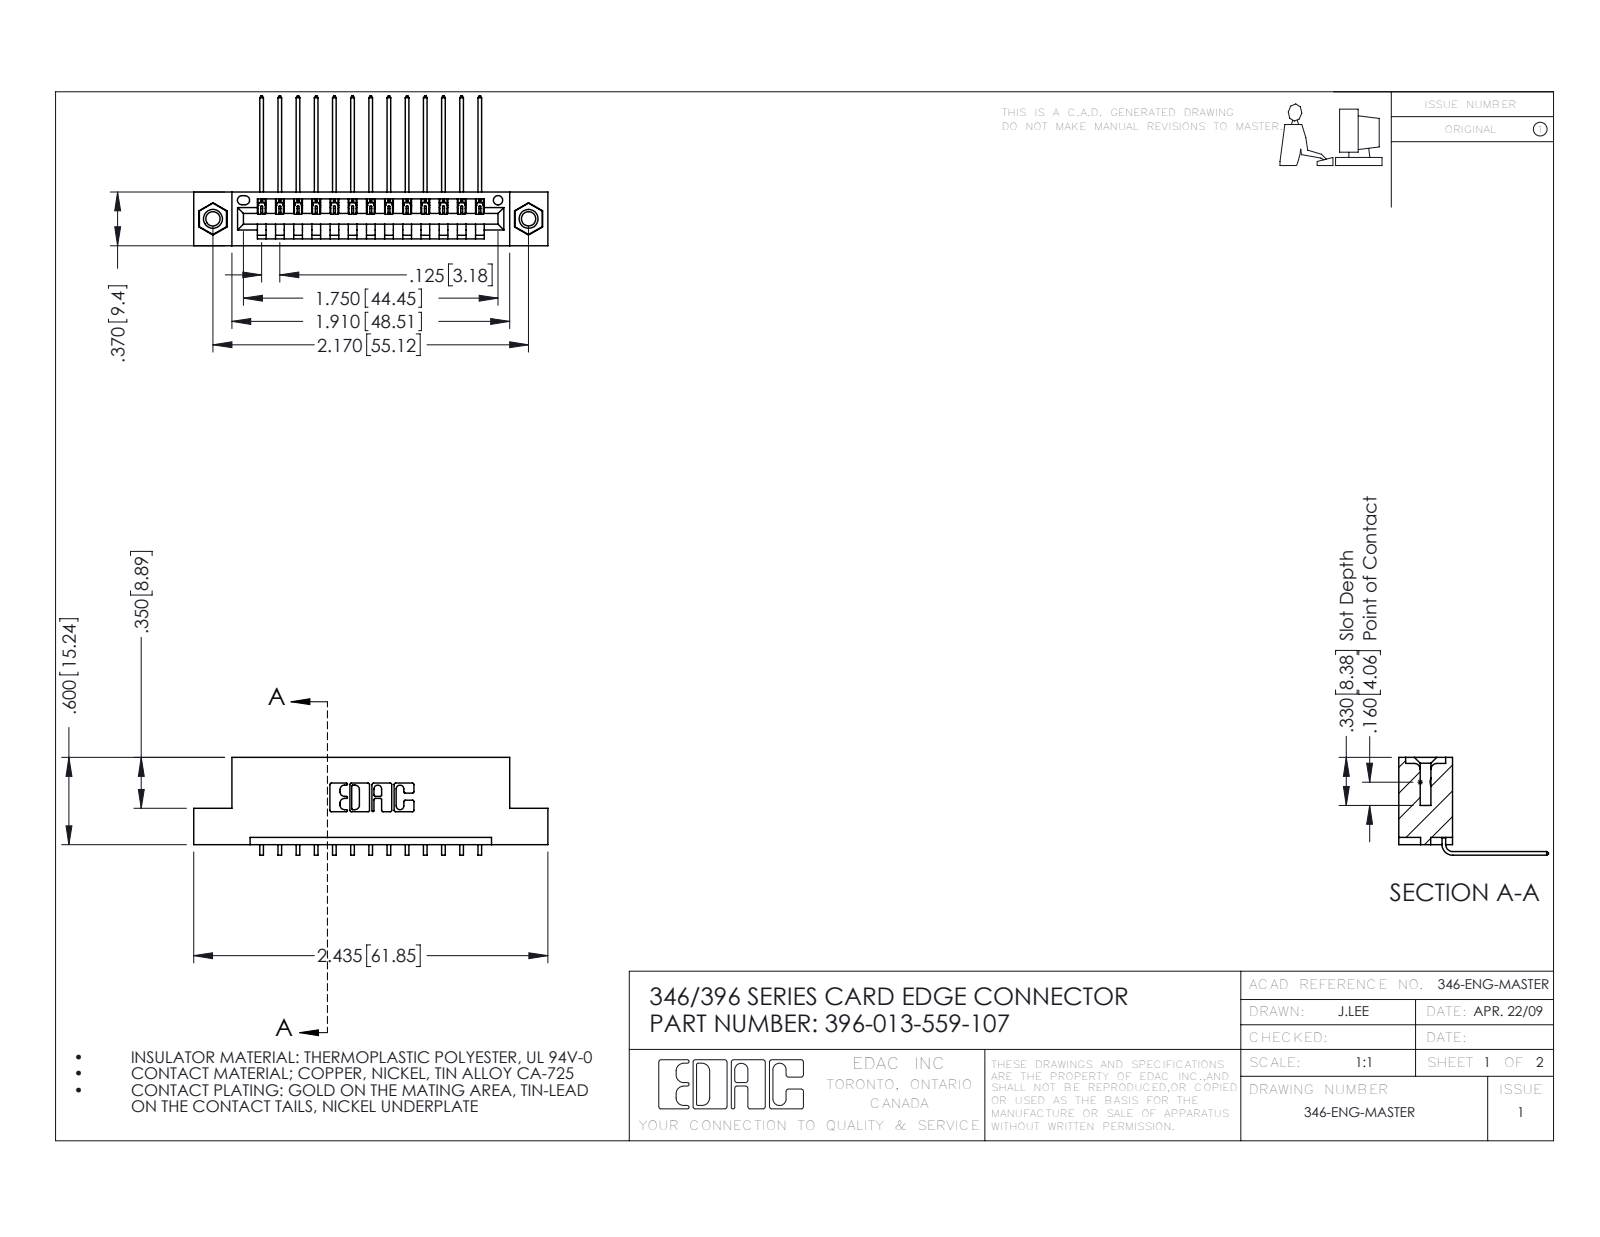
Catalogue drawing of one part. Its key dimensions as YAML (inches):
part_name: "396-013-559-107; 345-250-001_345-250-005-103; 345-292-001_558 559 Tail - 1; 346 Part_Flush Mounting Lugs - 0.156 Dia-TI"
step_written_by: "SolidWorks 2016 (CONFIG_CONTROL_DESIGN)"
units: inches
bodies: {solids: 16, faces: 962, planar: 654, cylindrical: 292, other: 16}
overall_size: [2.435, 1.03, 0.673]
volume: 0.351
surface_area: 11.11
round_holes:
  - {diameter: 0.098, count: 2}
  - {diameter: 0.125, count: 2}
  - {diameter: 0.156, count: 2}
  - {diameter: 0.064, count: 1}
round_bosses_or_shafts:
  - {diameter: 0.155, count: 2}
partial_cylinders:
  - {radius: 0.006, count: 26}
  - {radius: 0.01, count: 22}
  - {radius: 0.007, count: 6}
  - {radius: 0.031, count: 6}
  - {radius: 0.026, count: 3}
  - {radius: 0.031, count: 2}
  - {radius: 0.04, count: 2}
  - {radius: 0.014, count: 1}
face_to_face_distances: [0.048, 0.25, 0.322, 0.37, 0.072, 0.025, 0.298, 0.148, 0.222, 0.1]
hole_center_spacings: [0.246, 1.964, 2.17]
